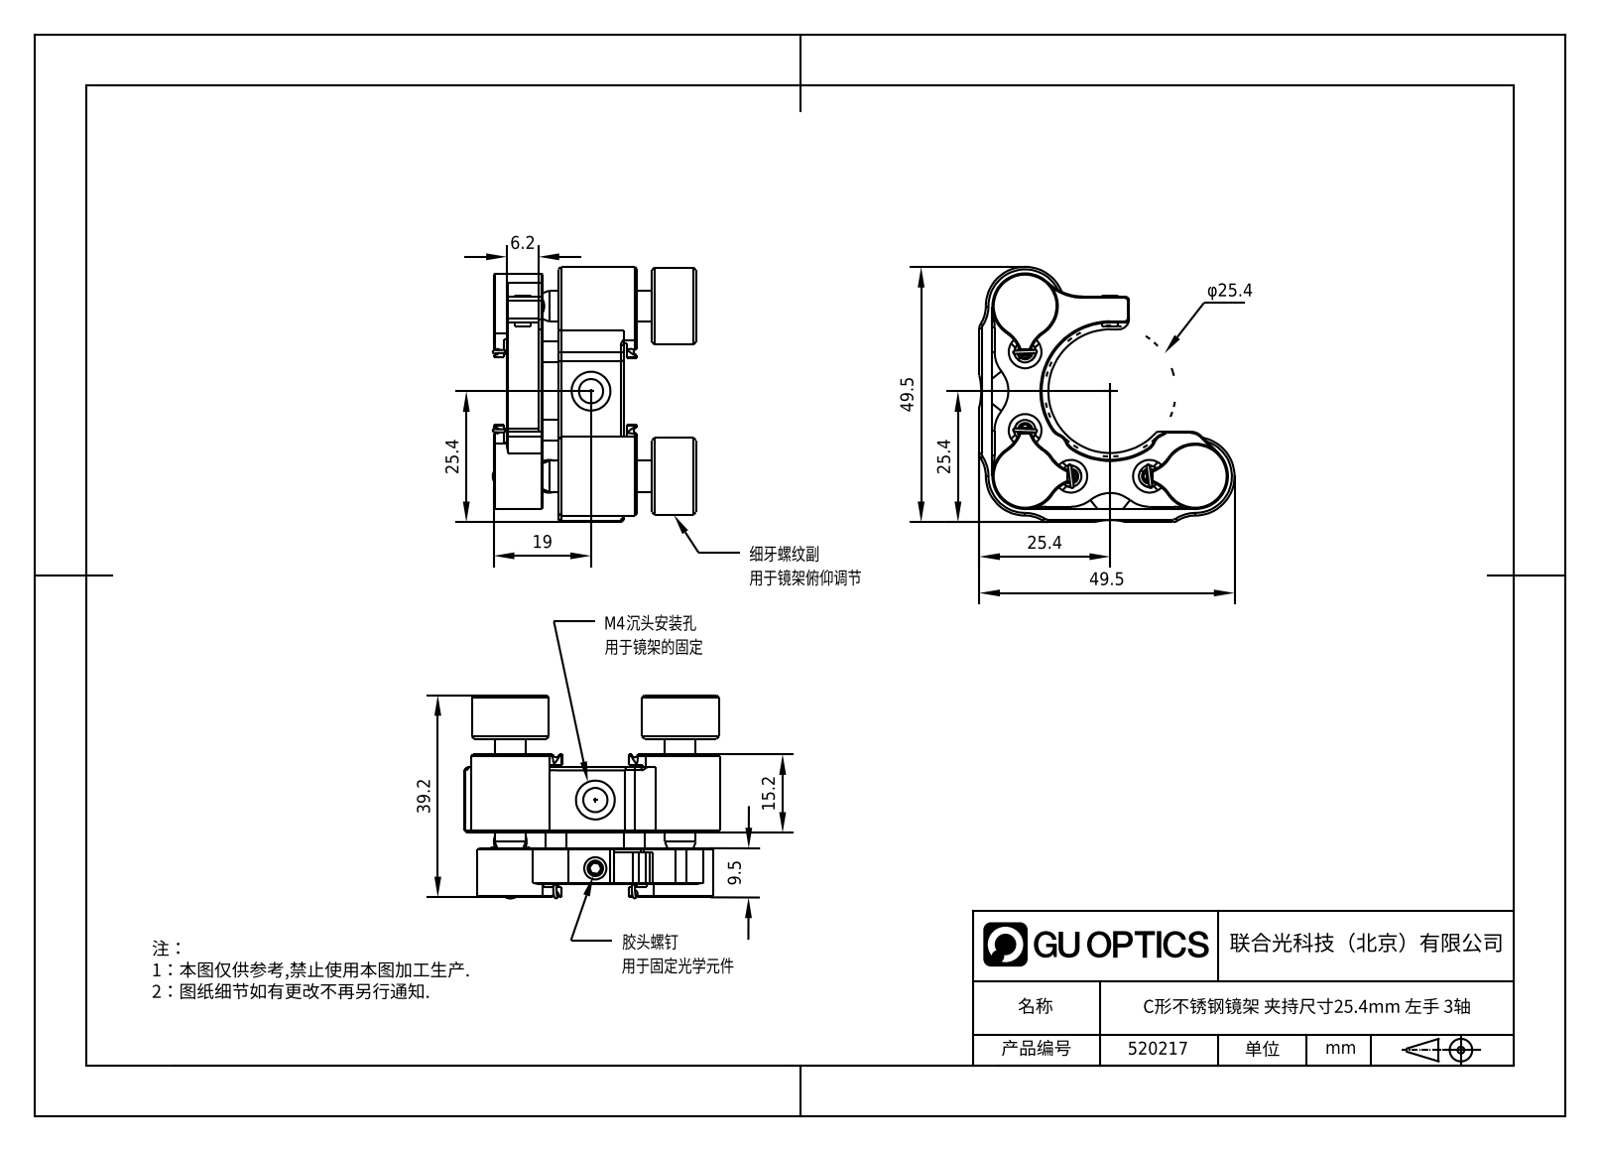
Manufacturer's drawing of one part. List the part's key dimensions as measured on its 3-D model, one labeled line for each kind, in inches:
Part name (STEP PRODUCT): 520217
STEP written by: SolidWorks 2020 (CONFIG_CONTROL_DESIGN)
Units: inches
Bodies: 26 solids, 554 faces (229 planar, 115 cylindrical, 210 other)
Overall size (bounding box): 1.95 × 1.95 × 1.595
Volume: 1.5 in³ · Surface area: 26.09 in²
Round holes (diameter × count): ⌀0.25 ×7, ⌀0.094 ×4, ⌀0.157 ×3, ⌀0.157 ×3, ⌀0.236 ×3, ⌀0.276 ×3, ⌀0.079 ×2, ⌀0.185 ×2, ⌀0.297 ×2, ⌀0.13 ×1
Round bosses / shafts (diameter × count): ⌀0.157 ×7, ⌀0.591 ×3, ⌀0.6 ×2, ⌀0.5 ×2, ⌀0.118 ×1
Partial cylindrical surfaces — rounded edges, fillets, slot ends (radius × count): R0.255 ×22, R0.118 ×5, R0.031 ×4, R0.039 ×4, R0.076 ×4, R0.125 ×4, R0.063 ×2, R0.063 ×2
Main face-to-face distances: 0.1, 0.993, 0.118, 0.878, 0.275, 0.718, 0.5, 0.6, 0.393, 1.488
Hole centre spacings: 0.35, 0.95, 0.197, 0.6, 1.013, 1.3, 1.346, 1.61
